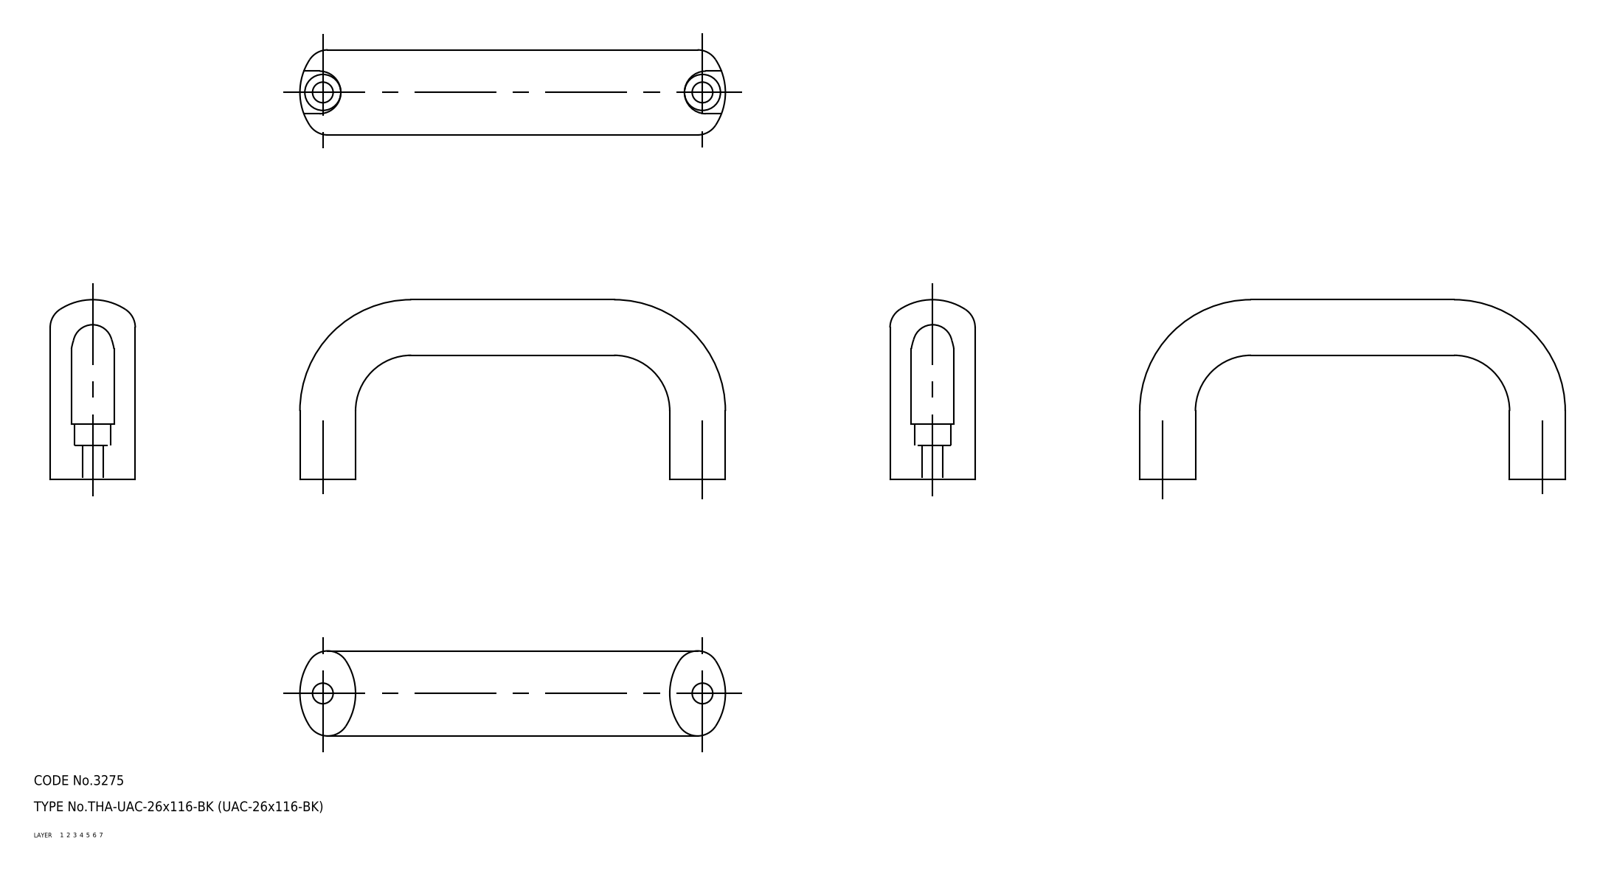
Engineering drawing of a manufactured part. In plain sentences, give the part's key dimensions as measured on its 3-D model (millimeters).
The part is named "67111523". Its 3-D file was written by "CADfix (AUTOMOTIVE_DESIGN)". It is 1 solid with 30 faces: 0 planar, 0 cylindrical and 30 other. Overall it measures 130 by 55 by 26 millimeters. Its volume is 56 073 cubic millimeters and its surface area 14 862 square millimeters.
